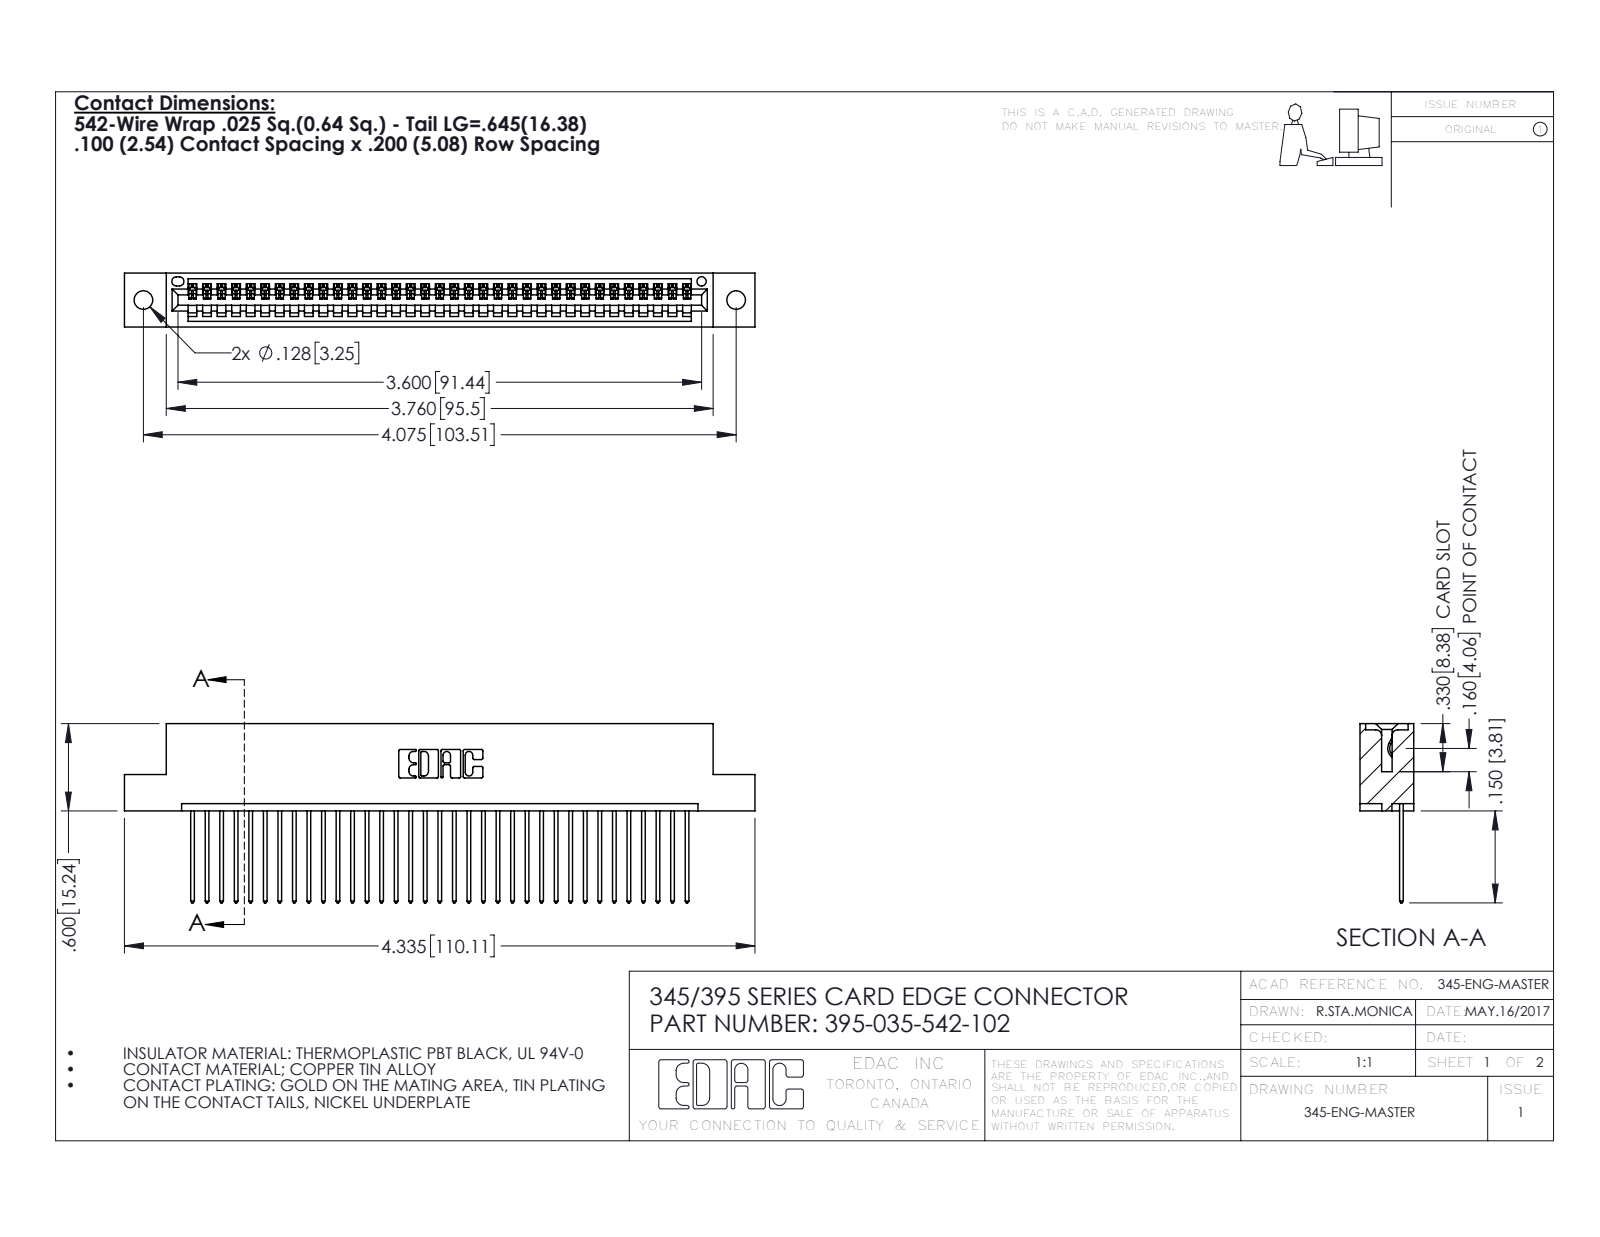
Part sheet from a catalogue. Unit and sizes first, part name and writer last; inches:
Units: inches
Overall size (bounding box): 4.335 × 1.232 × 0.37
Round holes (diameter × count): ⌀0.128 ×2, ⌀0.064 ×1
Partial cylindrical surfaces — rounded edges, fillets, slot ends (radius × count): R0.006 ×70, R0.01 ×70, R0.01 ×22, R0.007 ×6, R0.031 ×6, R0.026 ×3, R0.031 ×2, R0.04 ×2
Main face-to-face distances: 0.298, 0.072, 0.37, 0.098, 0.272, 0.025, 0.2, 0.225, 0.149, 0.072
Hole centre spacings: 0.27, 3.839, 4.075
Volume: 0.637 in³ · Surface area: 21.7 in²
Bodies: 36 solids, 2156 faces (1480 planar, 676 cylindrical, 0 other)
Part name (STEP PRODUCT): 345-292-001_345-293-142; 345 Part_Flush Mounting Lugs - 0.128 Dia; 395-035-542-102
STEP written by: SolidWorks 2016 (CONFIG_CONTROL_DESIGN)
